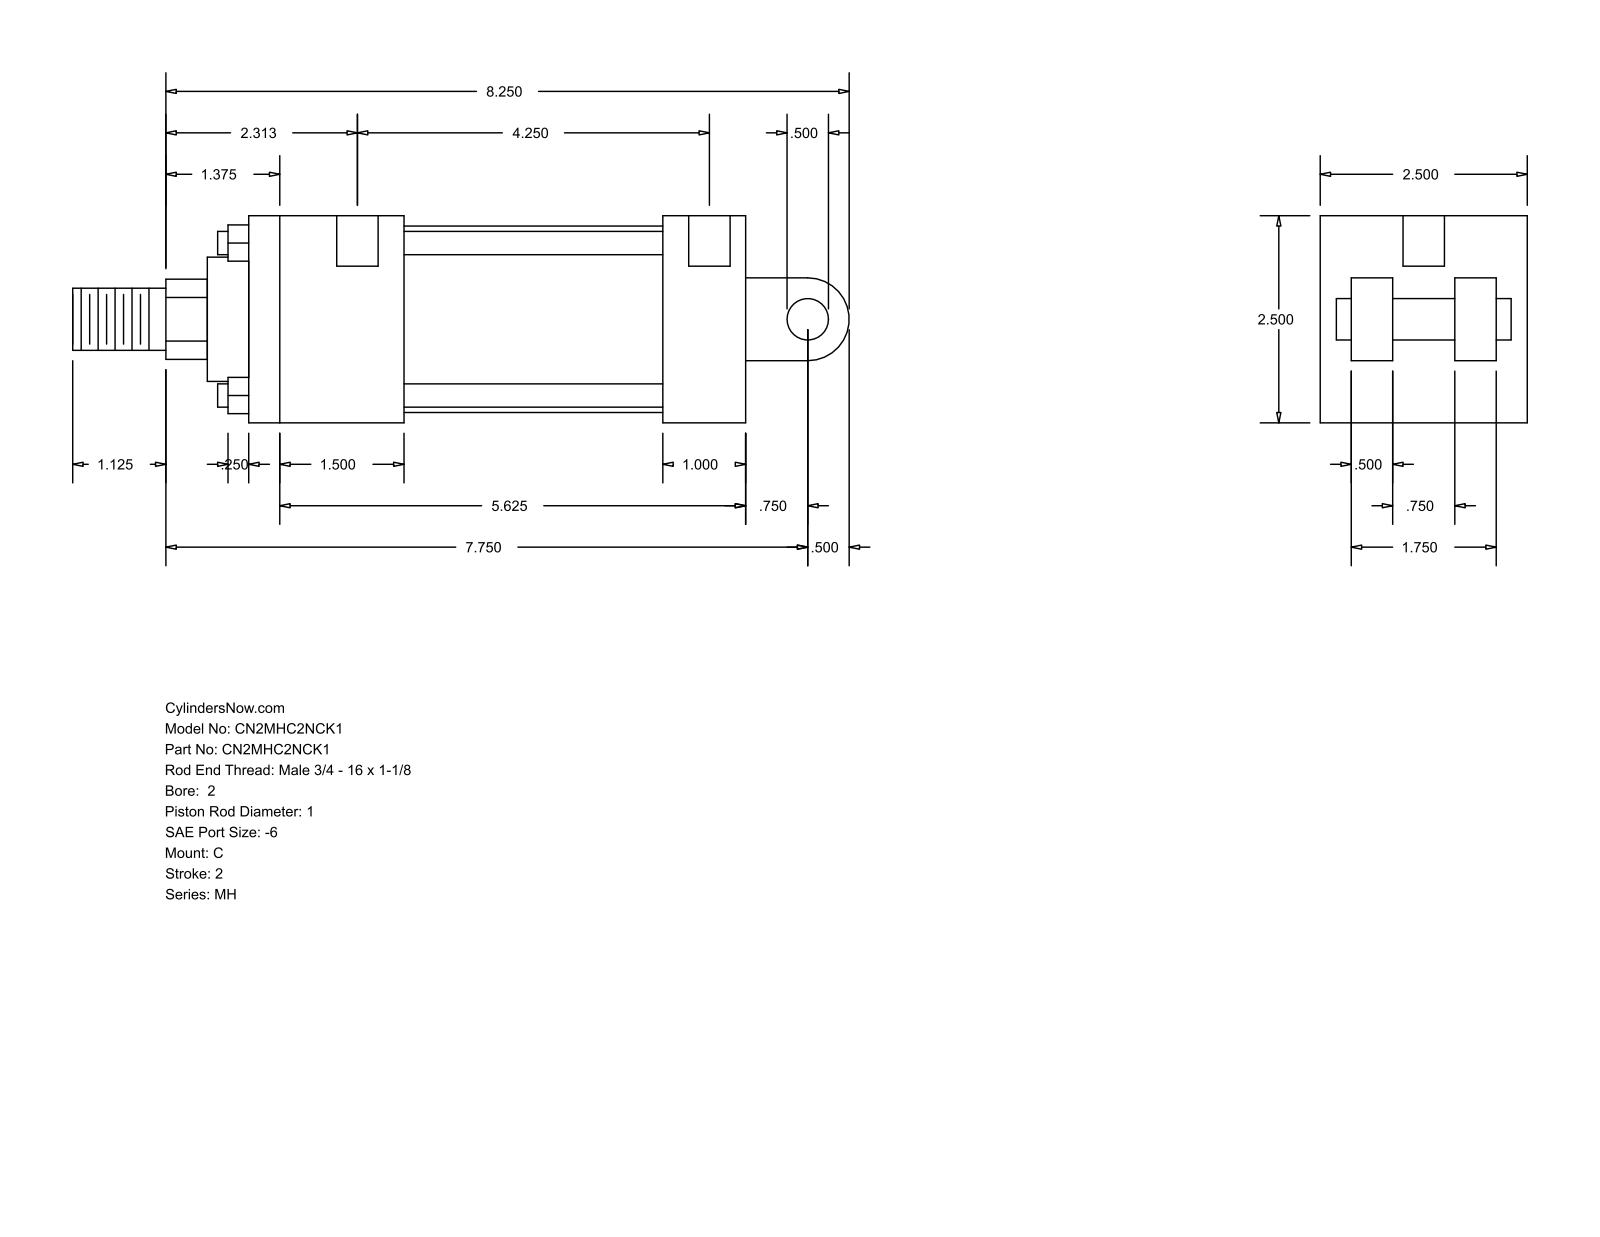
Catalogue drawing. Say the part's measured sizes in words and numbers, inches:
The part is named "MH_C__0200_1". Its 3-D file was written by "GSSL Pune (CONFIG_CONTROL_DESIGN)". It is 0 solids with 99 faces: 70 planar, 29 cylindrical and 0 other. Overall it measures 9.375 by 2.5 by 2.5 inches. Round holes: 4 of diameter 0.219, 2 of diameter 0.5. Round bosses or shafts: 4 of diameter 0.281, 1 of diameter 2.25, 1 of diameter 1.5, 1 of diameter 1, 1 of diameter 0.75, 1 of diameter 0.5. Partial cylindrical surfaces (rounded edges, fillets, slot ends): 1 of radius 0.484, 1 of radius 0.5. The main face-to-face distances are 2.5, 6, 0.5, 1, 1.875, 2.125, 0.375, 5, 3.125, 4.125. The hole center spacings are 4.562, 0.125, 0.187, 4.25, 4.375, 4.437.
